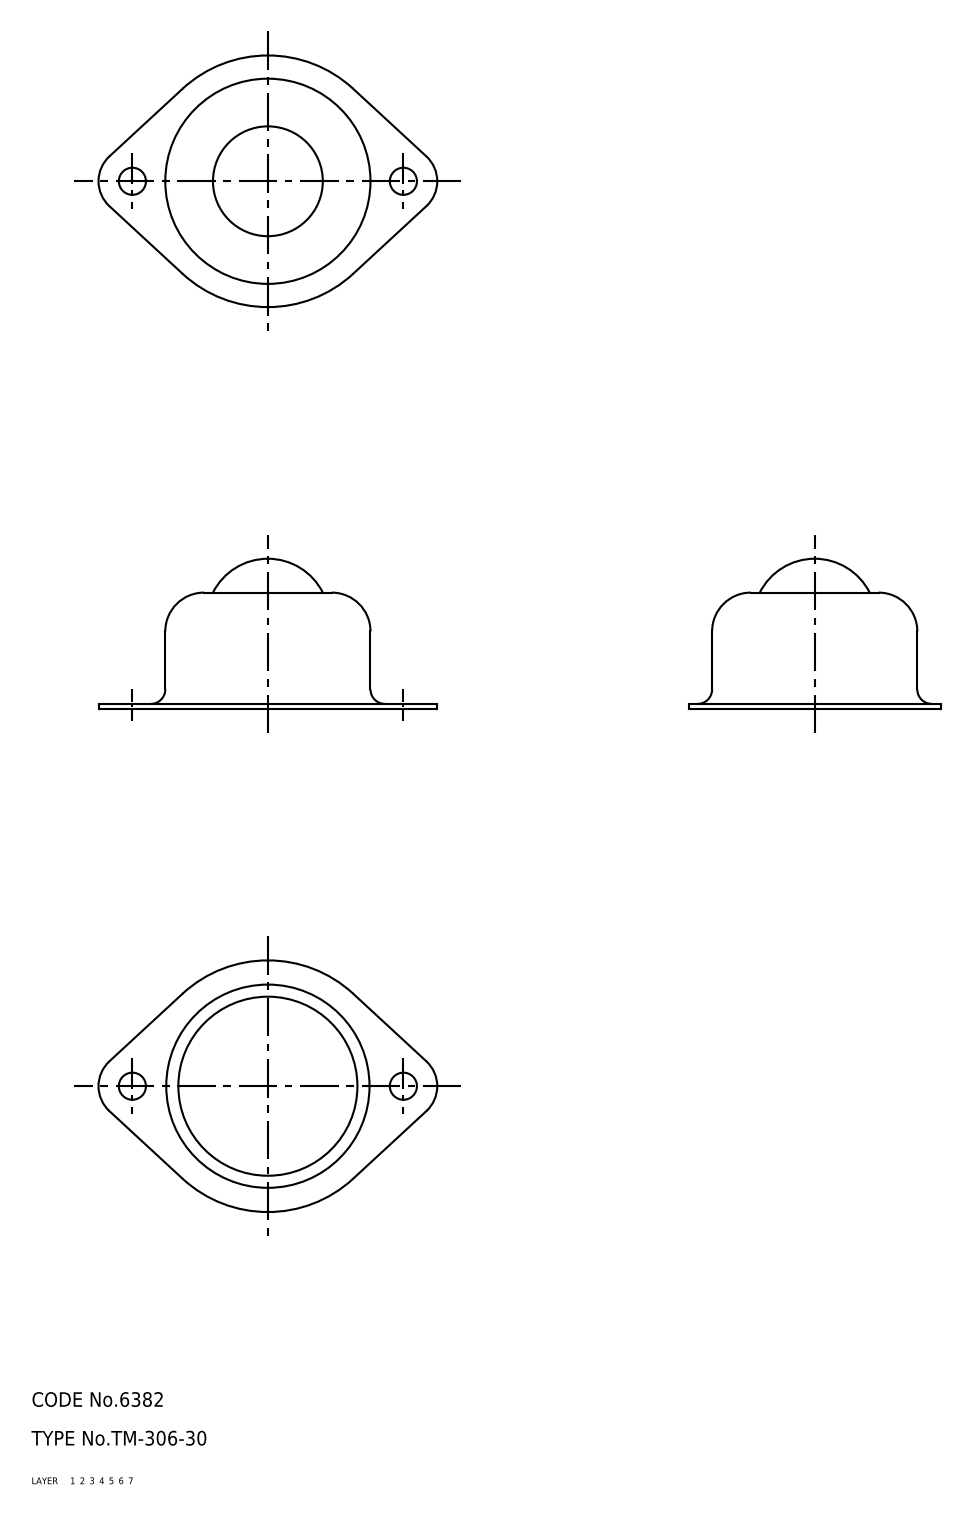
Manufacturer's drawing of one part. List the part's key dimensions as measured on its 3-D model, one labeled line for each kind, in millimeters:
Part name (STEP PRODUCT): 67113083; 67113096; 67113109
STEP written by: CADfix (AUTOMOTIVE_DESIGN)
Units: millimetres
Bodies: 3 solids, 50 faces (0 planar, 0 cylindrical, 50 other)
Overall size (bounding box): 70 × 52 × 31
Volume: 16 145 mm³ · Surface area: 17 590 mm²
